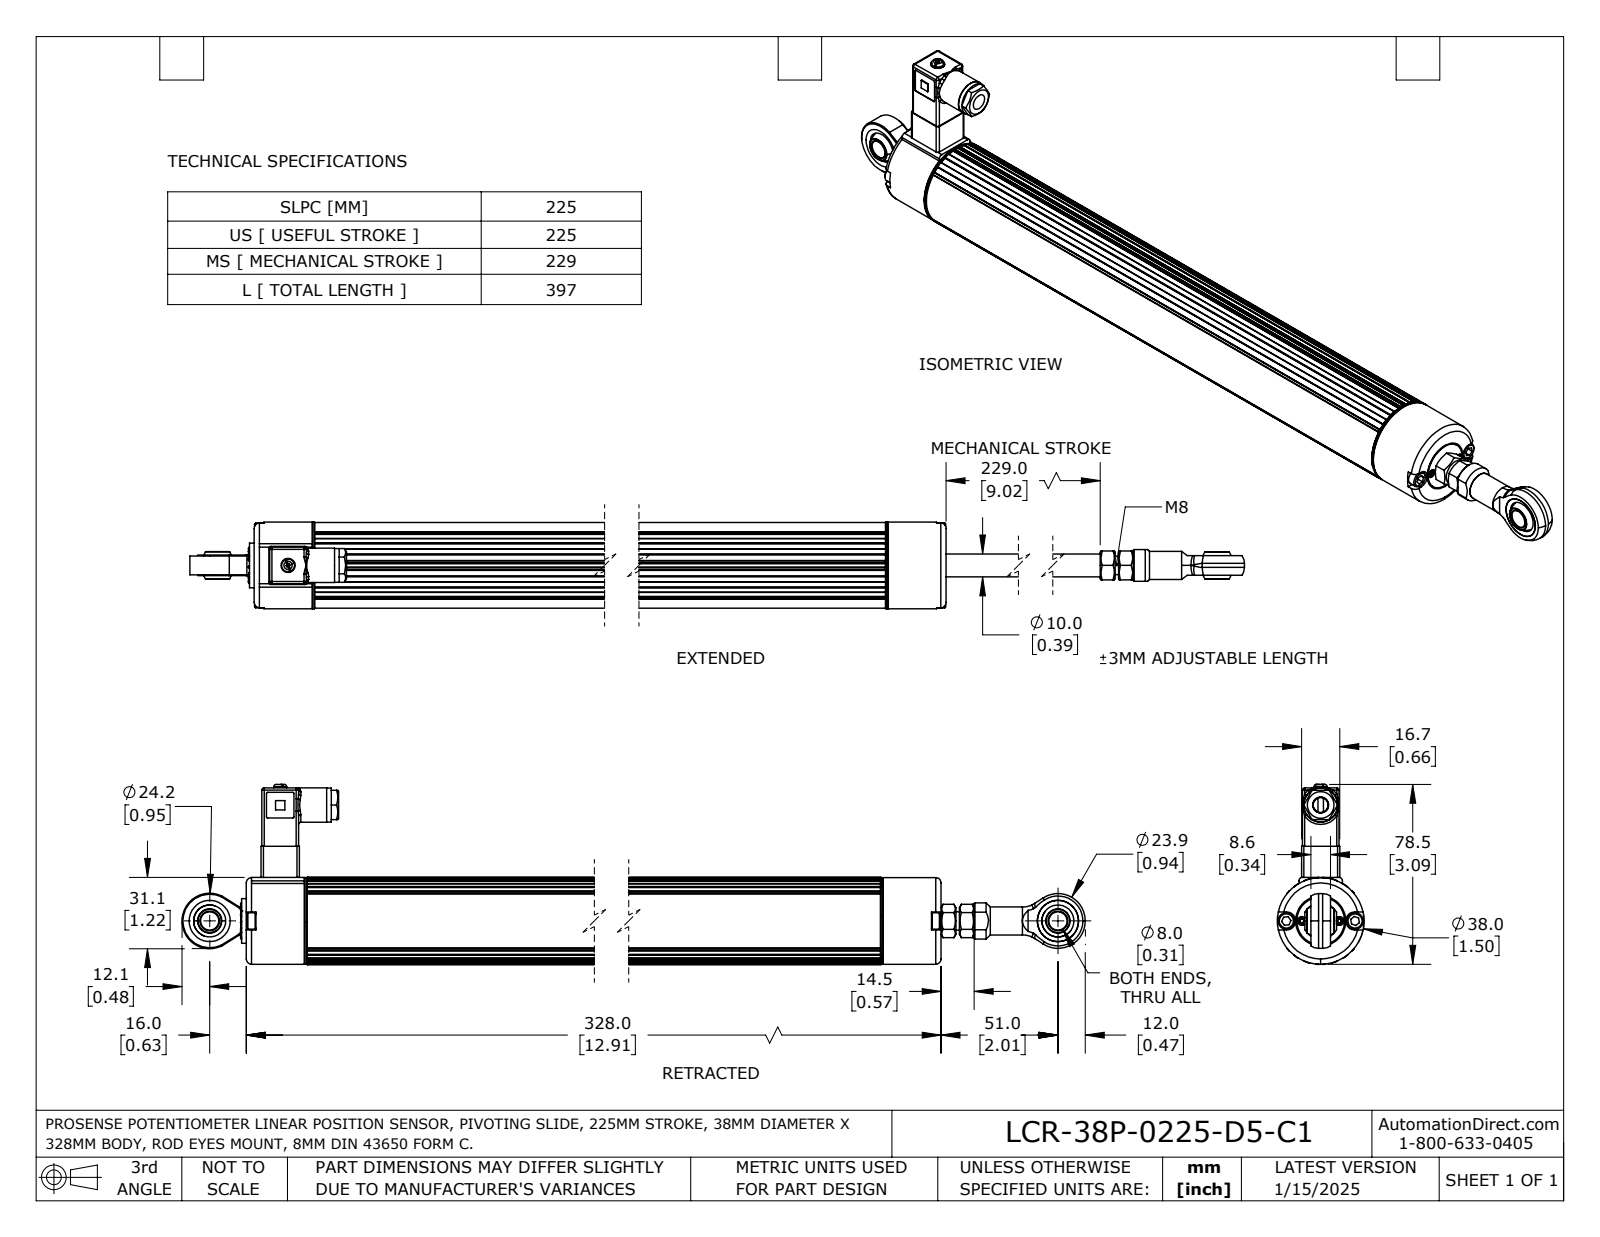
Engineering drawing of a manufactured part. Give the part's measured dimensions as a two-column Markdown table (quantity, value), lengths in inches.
| quantity | value |
| --- | --- |
| part name | LCR-38P-0225-D5-C1 |
| STEP written by | SolidWorks 2023 (AUTOMOTIVE_DESIGN) |
| units | inches |
| bodies | 11 solids, 657 faces (295 planar, 210 cylindrical, 152 other) |
| overall size | 16.498 × 3.093 × 1.488 |
| volume | 23.31 in³ |
| surface area | 114.1 in² |
| round holes (diameter × count) | 0.102 × 6, 0.091 × 4, 0.315 × 3, 0.551 × 3, 0.094 × 2, 0.1 × 2, 0.111 × 2, 0.134 × 2, 0.152 × 2, 0.165 × 2, 0.079 × 1, 0.118 × 1 |
| round bosses / shafts (diameter × count) | 0.063 × 6, 0.283 × 4, 0.15 × 4, 0.48 × 2, 0.079 × 2, 1.488 × 1, 0.823 × 1, 0.768 × 1 |
| partial cylindrical surfaces (radius × count) | 0.008 × 32, 0.039 × 20, 0.02 × 12, 0.016 × 6, 0.012 × 2, 0.059 × 2, 0.083 × 2, 0.098 × 2 |
| main face-to-face distances | 10.827, 1.043, 11.87, 0.031, 0.045, 0.612, 0.598, 0.014, 0.644, 0.138 |
| hole center spacings | 0.632, 0.075, 0.634, 0.264, 0.268, 0.285, 0.323, 0.394 |
